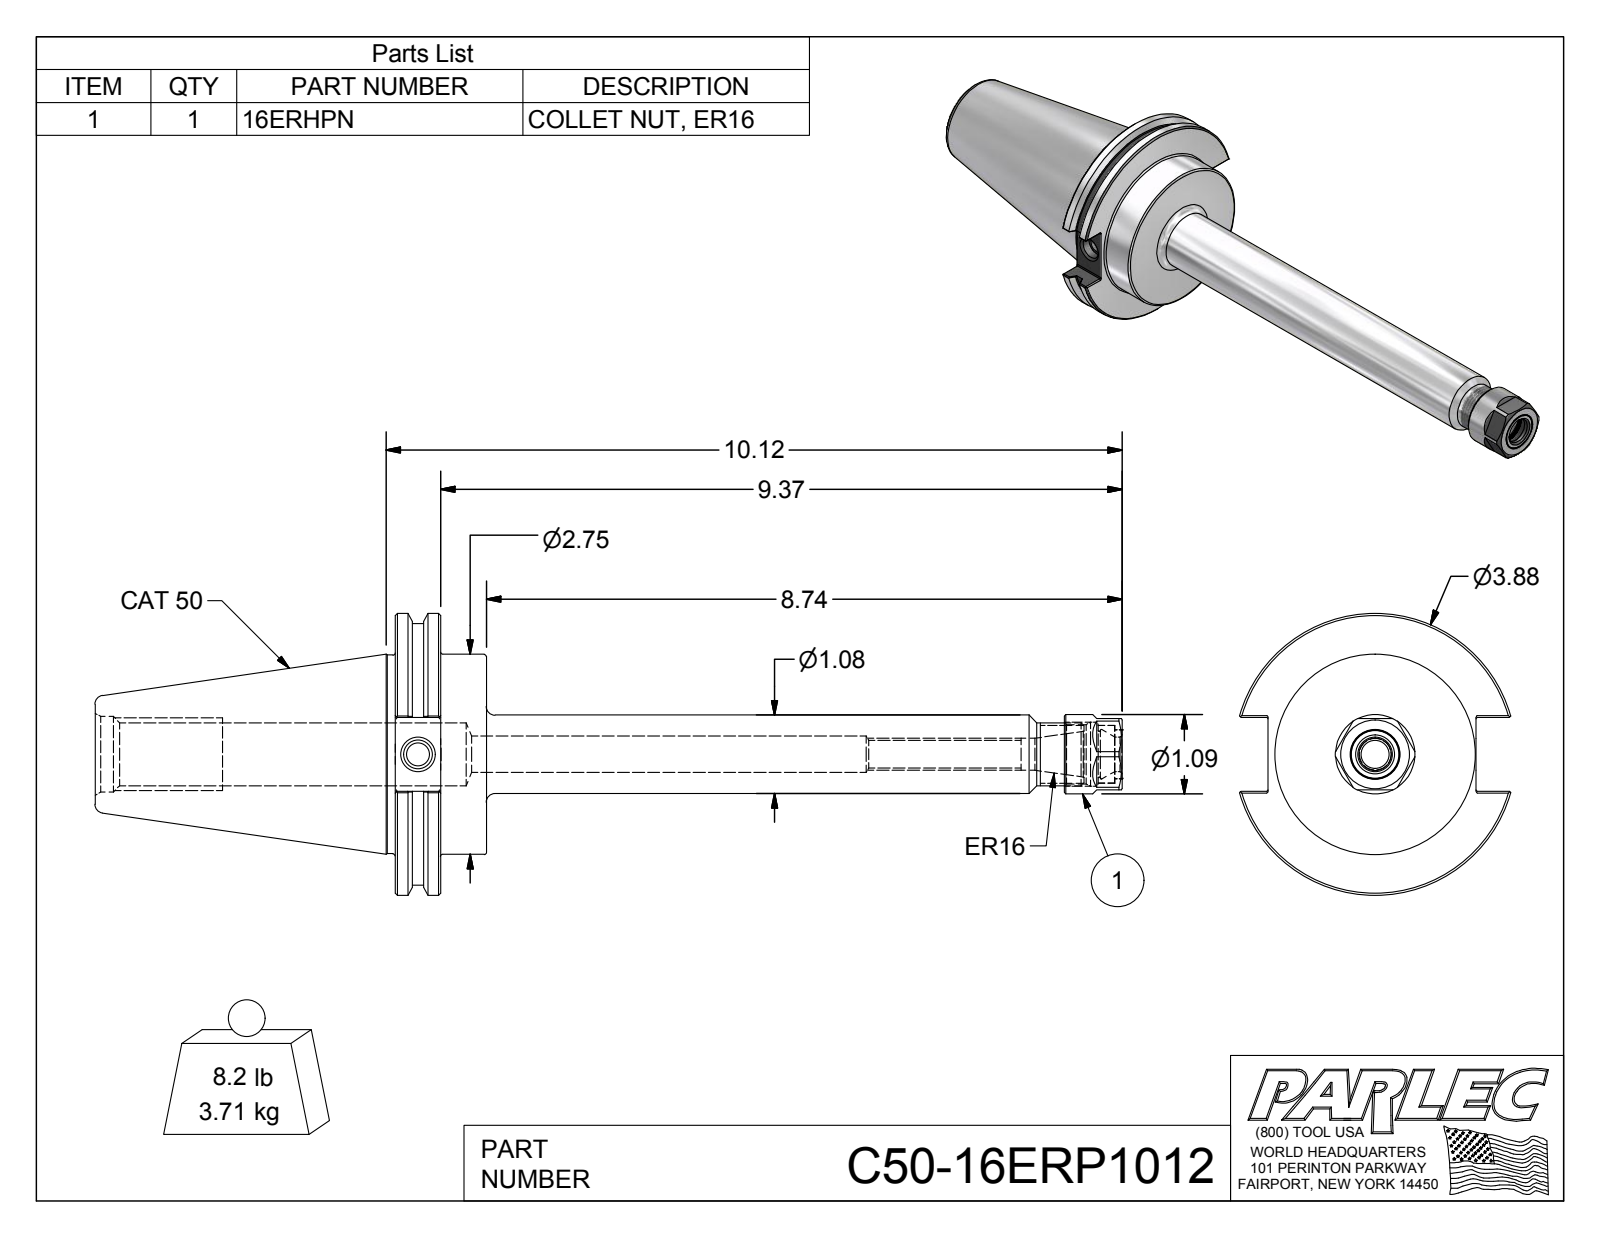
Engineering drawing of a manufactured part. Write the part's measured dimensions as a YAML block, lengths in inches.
part_name: "C50-16ERP1012; C50-16ER10-1; 16ERHPN"
step_written_by: "Autodesk Inventor 2012 (AUTOMOTIVE_DESIGN)"
units: inches
bodies: {solids: 3, faces: 138, planar: 53, cylindrical: 39, other: 46}
overall_size: [14.12, 3.875, 3.729]
volume: 29.05
surface_area: 122.1
round_holes:
  - {diameter: 0.315, count: 1}
  - {diameter: 0.383, count: 1}
  - {diameter: 0.399, count: 1}
  - {diameter: 0.44, count: 1}
  - {diameter: 0.474, count: 1}
  - {diameter: 0.5, count: 1}
  - {diameter: 0.63, count: 1}
  - {diameter: 0.674, count: 1}
  - {diameter: 0.68, count: 1}
  - {diameter: 0.794, count: 1}
  - {diameter: 0.814, count: 1}
  - {diameter: 0.865, count: 1}
round_bosses_or_shafts:
  - {diameter: 3.875, count: 1}
  - {diameter: 3.594, count: 1}
  - {diameter: 2.75, count: 1}
  - {diameter: 2.73, count: 1}
  - {diameter: 1.092, count: 1}
  - {diameter: 1.08, count: 1}
  - {diameter: 0.866, count: 1}
  - {diameter: 0.79, count: 1}
partial_cylinders:
  - {radius: 0.02, count: 12}
face_to_face_distances: [1.255, 0.625, 0.63, 4.125, 4.75, 5.38, 0.98, 14.12, 9.995, 9.37]
